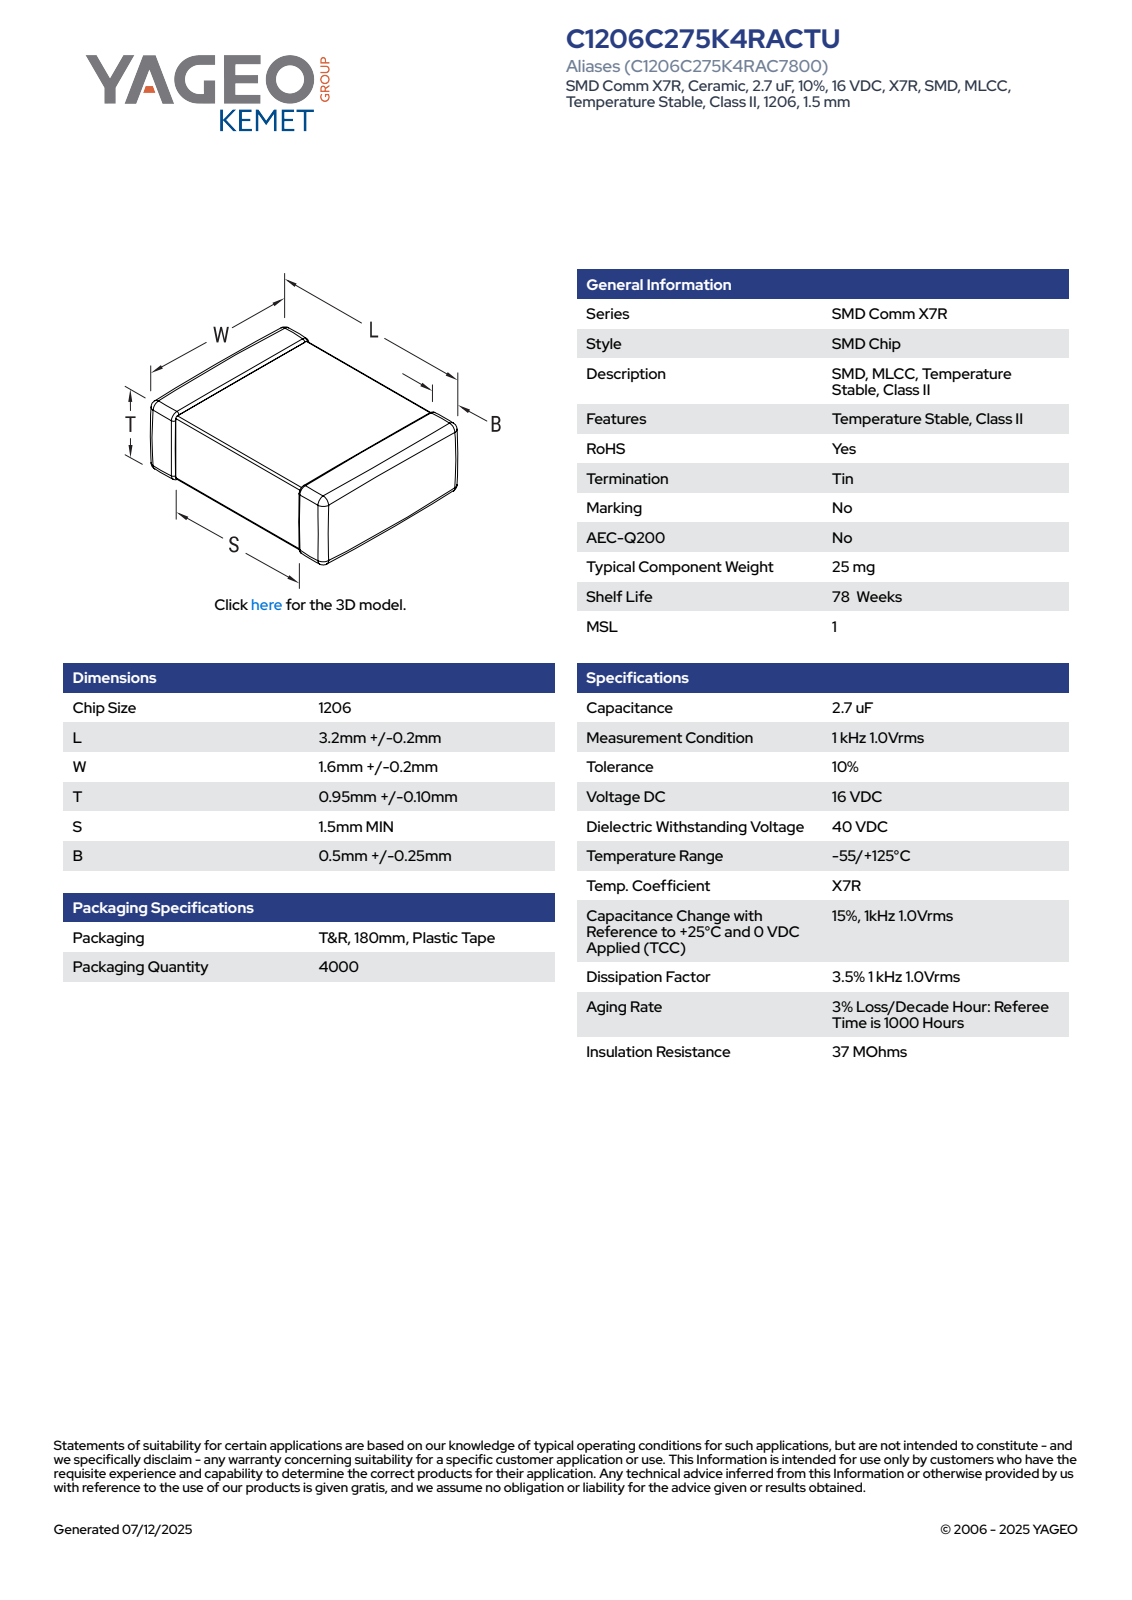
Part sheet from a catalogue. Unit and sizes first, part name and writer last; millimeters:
Units: millimetres
Overall size (bounding box): 3.4 × 1.8 × 1.05
Main face-to-face distances: 1.01, 0.97, 1.76, 1.05, 1.72, 3.4, 1.8, 0.98, 1.02, 0.99
Volume: 6 mm³ · Surface area: 23 mm²
Bodies: 4 solids, 125 faces (71 planar, 38 cylindrical, 16 other)
Part name (STEP PRODUCT): CCS_CCSTDNOS_1206_L3.4W1.8T1.05B0.75
STEP written by: SolidWorks 2014 (AUTOMOTIVE_DESIGN)
